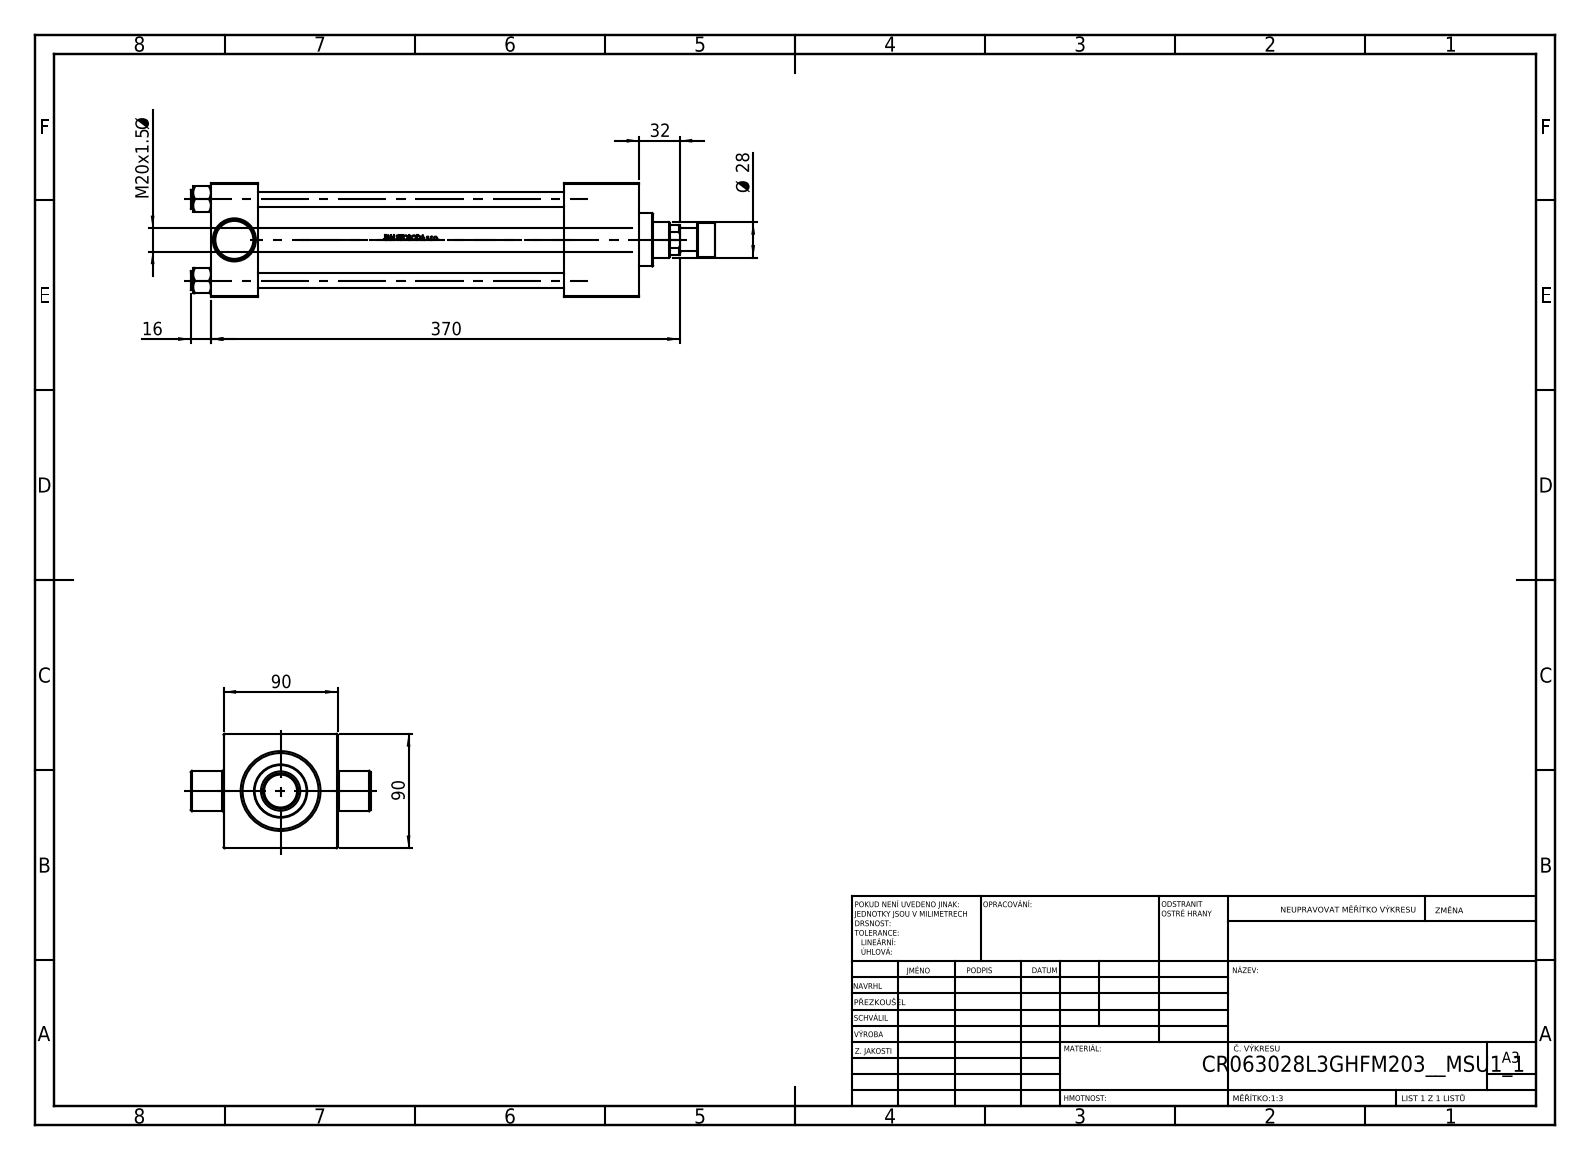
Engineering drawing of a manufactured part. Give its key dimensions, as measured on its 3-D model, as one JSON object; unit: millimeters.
{"part_name": "V215CR_L_TYCINKA; V215CR_ROD_END_F; V215_VC_A; V215CR_L_Body (+2 more)", "step_written_by": "SolidWorks 2019 (CONFIG_CONTROL_DESIGN)", "units": "millimeters", "bodies": {"solids": 12, "faces": 1071, "planar": 429, "cylindrical": 114, "other": 528}, "overall_size": [414, 142, 90], "volume_mm3": 1324000, "surface_area_mm2": 299557, "round_holes": [[12, 4], [7, 1], [18.5, 1], [28, 1], [31, 1], [50, 1], [60, 1], [63, 1]], "round_bosses_or_shafts": [[15, 4], [69, 1], [42, 1], [32, 1], [27, 1], [18, 1]], "face_to_face_distances": [90, 37, 338, 301, 89, 59, 0.5, 242, 279, 89.5], "hole_center_spacings": [45.47, 64.3, 90.93]}
